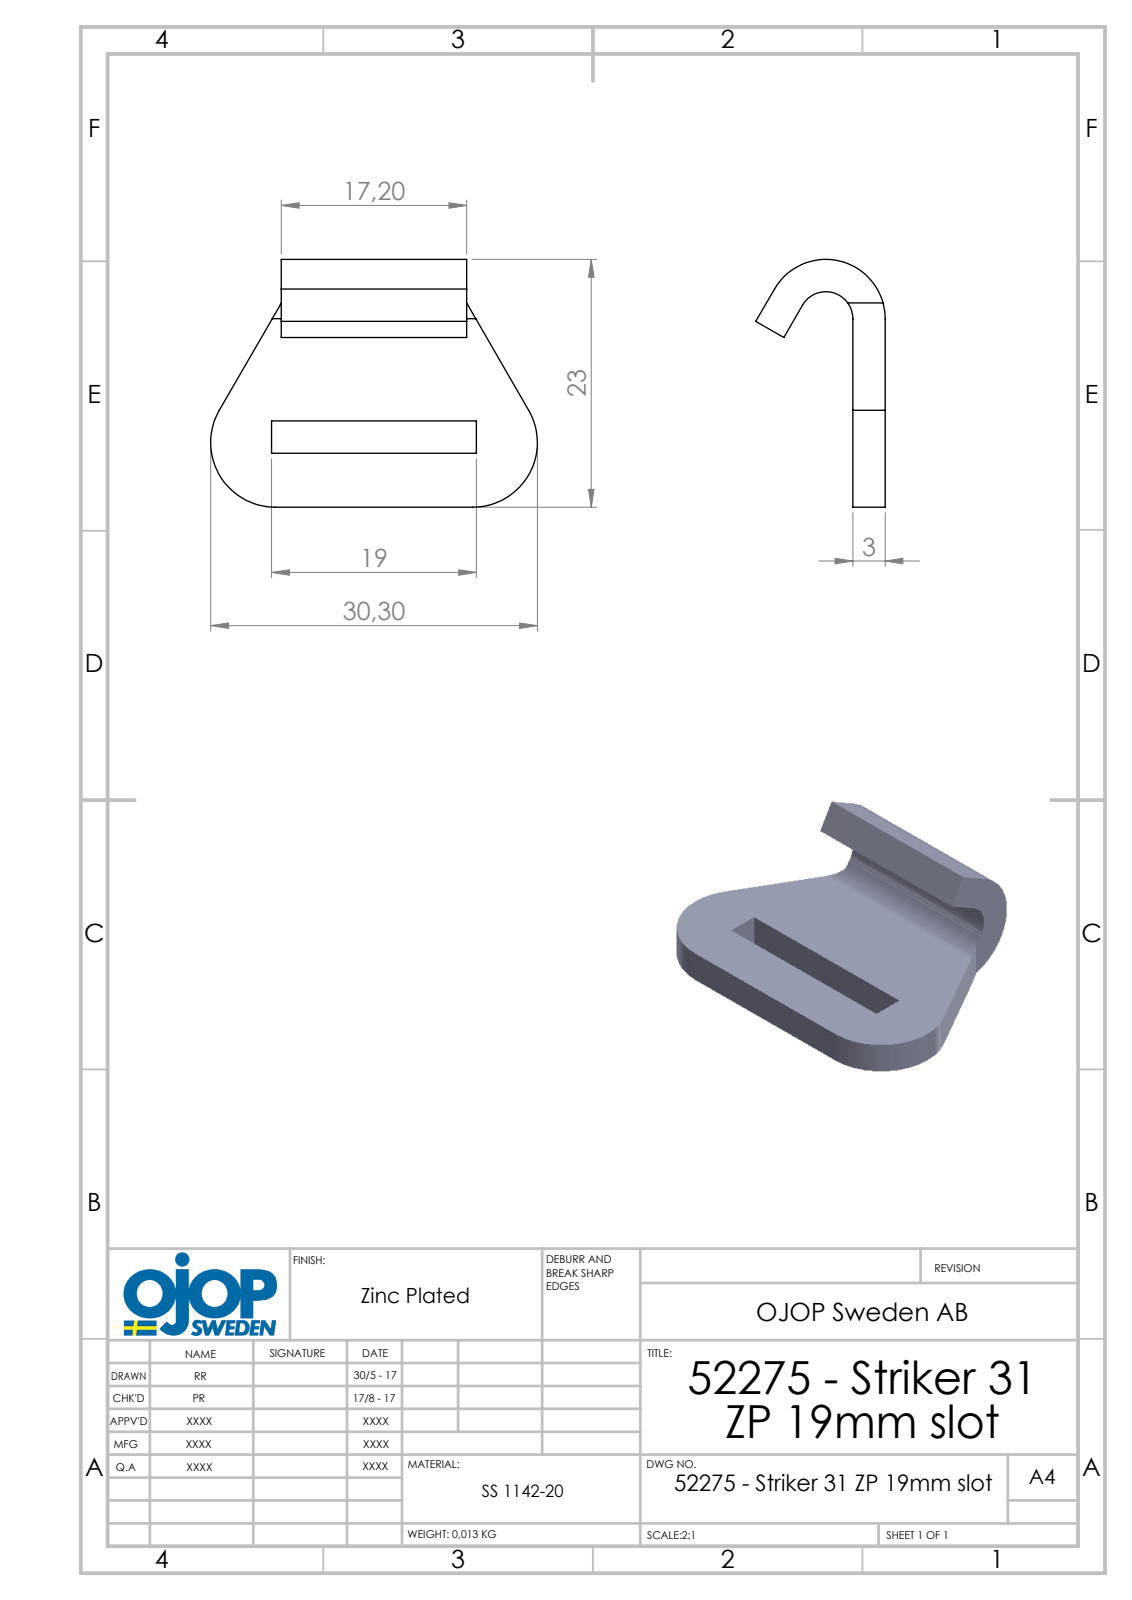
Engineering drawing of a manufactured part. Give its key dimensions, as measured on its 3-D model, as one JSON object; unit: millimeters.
{"part_name": "52275 - Striker 31 ZP 19mm slot", "step_written_by": "SolidWorks 2015 (AUTOMOTIVE_DESIGN)", "units": "millimeters", "bodies": {"solids": 1, "faces": 18, "planar": 14, "cylindrical": 4, "other": 0}, "overall_size": [30.3, 23, 12], "volume_mm3": 1926, "surface_area_mm2": 1742, "partial_cylinders_radius": [[6, 2], [2.5, 1], [5.5, 1]], "face_to_face_distances": [3, 8, 5, 17.2, 0.9, 18.1, 19]}
